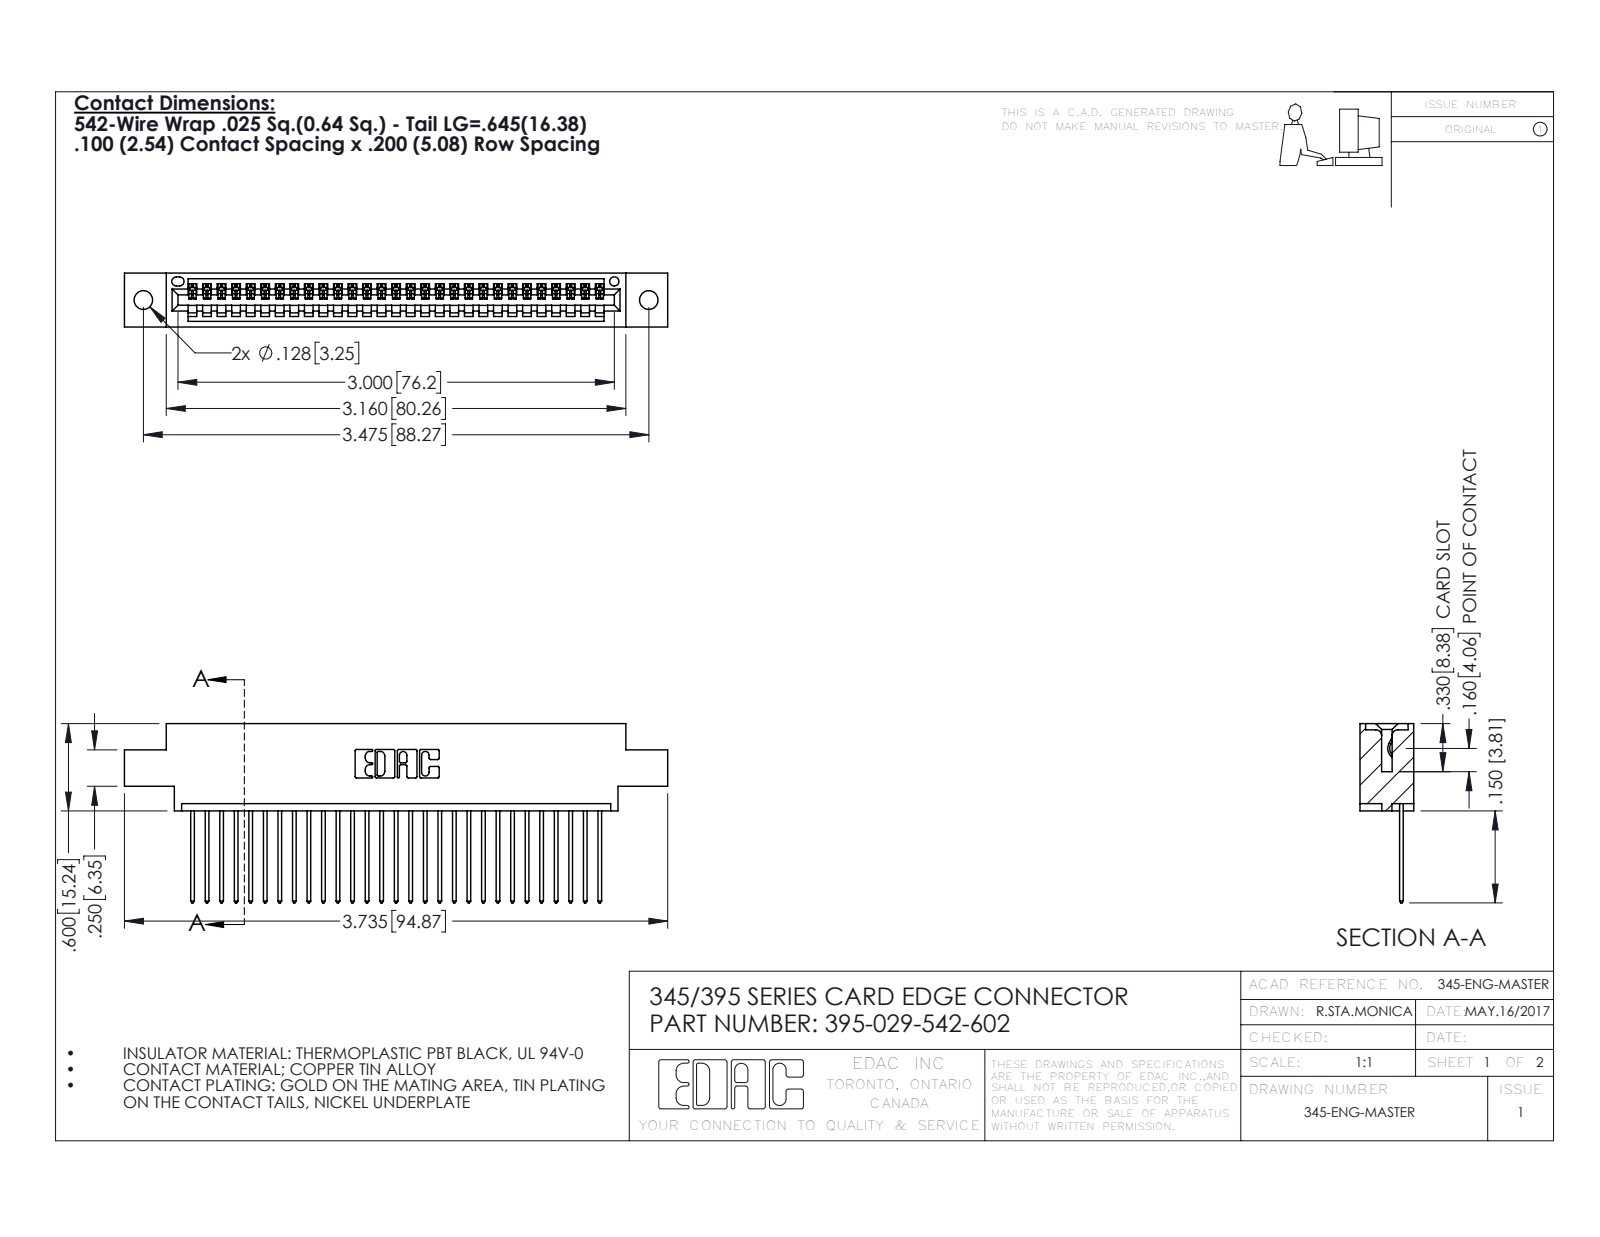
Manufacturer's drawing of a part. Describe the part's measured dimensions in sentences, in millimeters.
The part is named "395-029-542-602; 345-292-001_345-293-142; 345 Part_0.170 Offset - 0.128 Dia". Its 3-D file was written by "SolidWorks 2016 (CONFIG_CONTROL_DESIGN)". It is 30 solids with 1812 faces: 1244 planar, 568 cylindrical and 0 other. Overall it measures 94.9 by 31.3 by 9.4 millimeters. Its volume is 8 820 cubic millimeters and its surface area 11 810 square millimeters. Round holes: 2 of diameter 3.3, 1 of diameter 1.6. Partial cylindrical surfaces (rounded edges, fillets, slot ends): 58 of radius 0.2, 58 of radius 0.3, 22 of radius 0.3, 6 of radius 0.2, 6 of radius 0.8, 3 of radius 0.7, 2 of radius 0.8, 2 of radius 1. The main face-to-face distances are 7.6, 1.8, 9.4, 2.5, 6.9, 0.6, 5.1, 5.7, 4.4, 3.8. The hole center spacings are 6.9, 82.3, 88.3.
